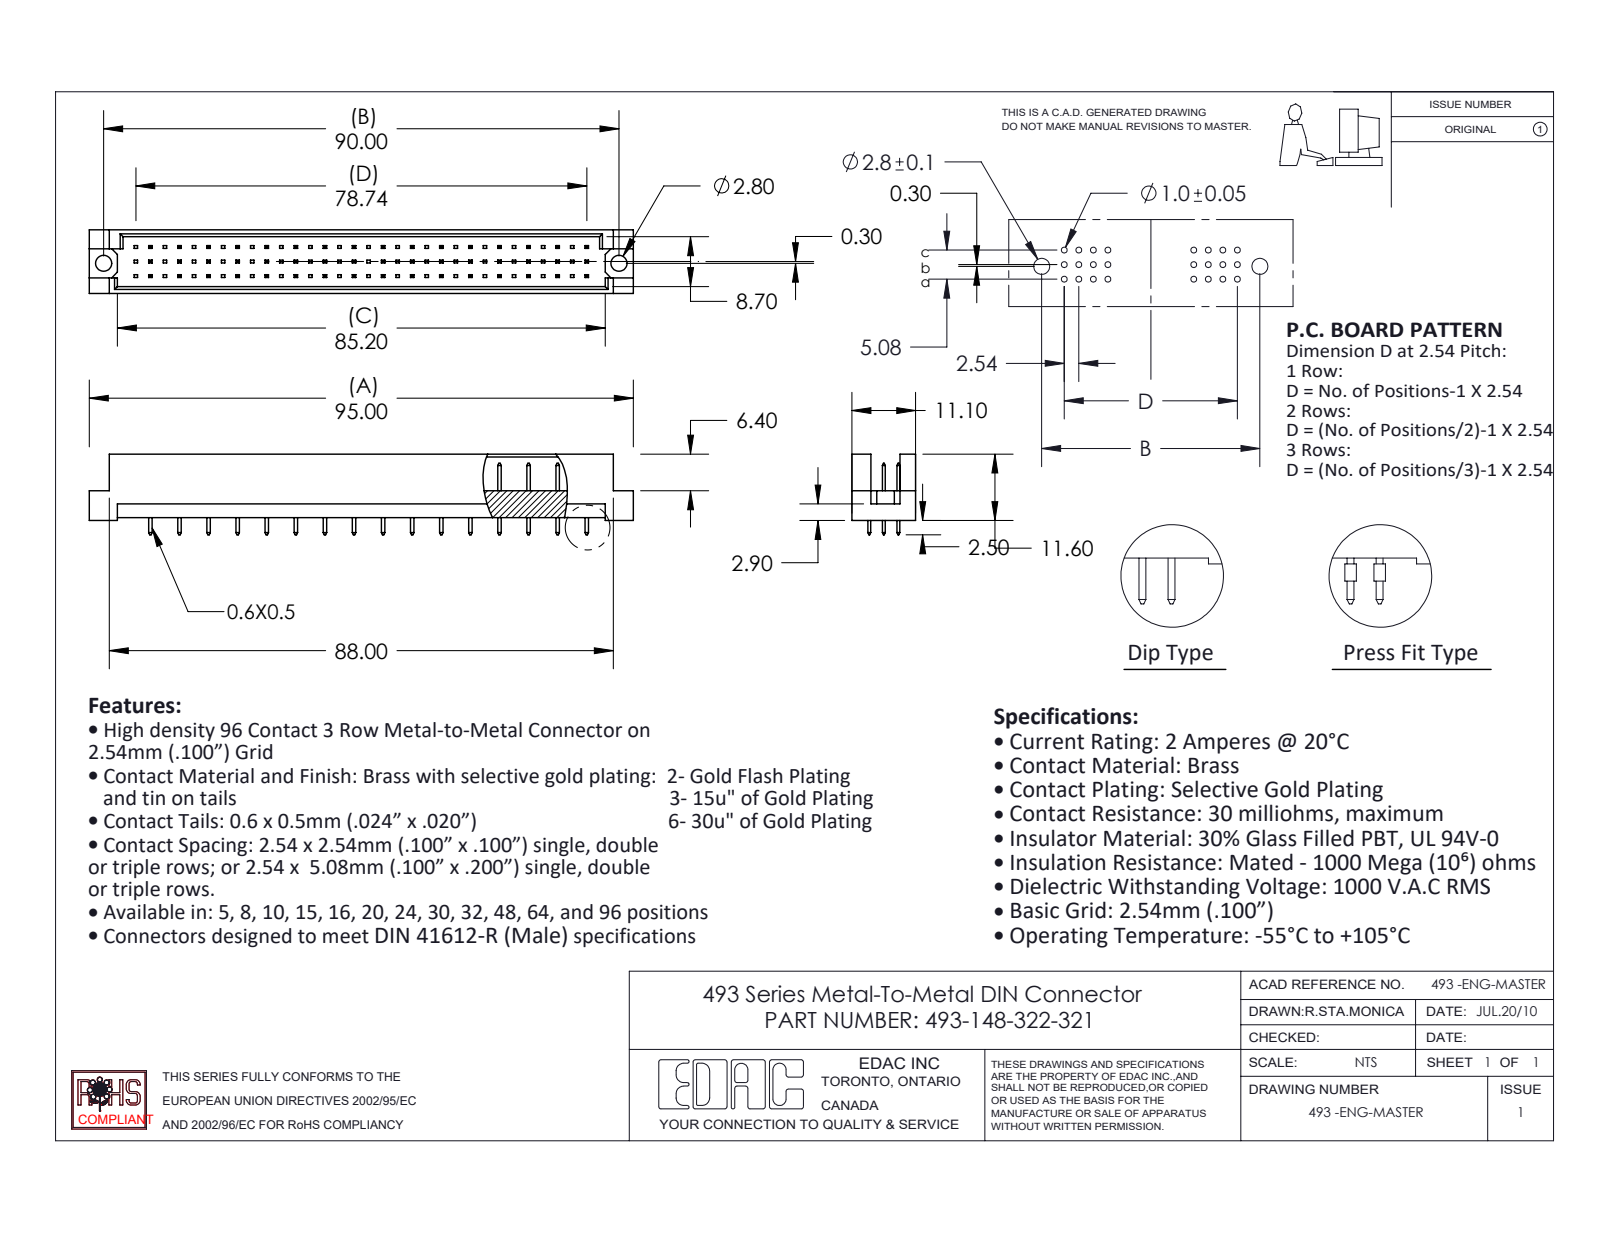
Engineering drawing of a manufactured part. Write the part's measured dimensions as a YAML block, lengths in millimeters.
part_name: "493-148-322-321; 493-290_22; 493 Part_96"
step_written_by: "SolidWorks 2020 (CONFIG_CONTROL_DESIGN)"
units: millimeters
bodies: {solids: 49, faces: 1108, planar: 1104, cylindrical: 4, other: 0}
overall_size: [95, 14.1, 11.1]
volume: 5834
surface_area: 7776
round_holes:
  - {diameter: 2.8, count: 2}
face_to_face_distances: [1.2, 9.9, 11.1, 8.7, 2.54, 5.08, 4.7, 0.5, 2.76, 3.26]
hole_center_spacings: [90]
